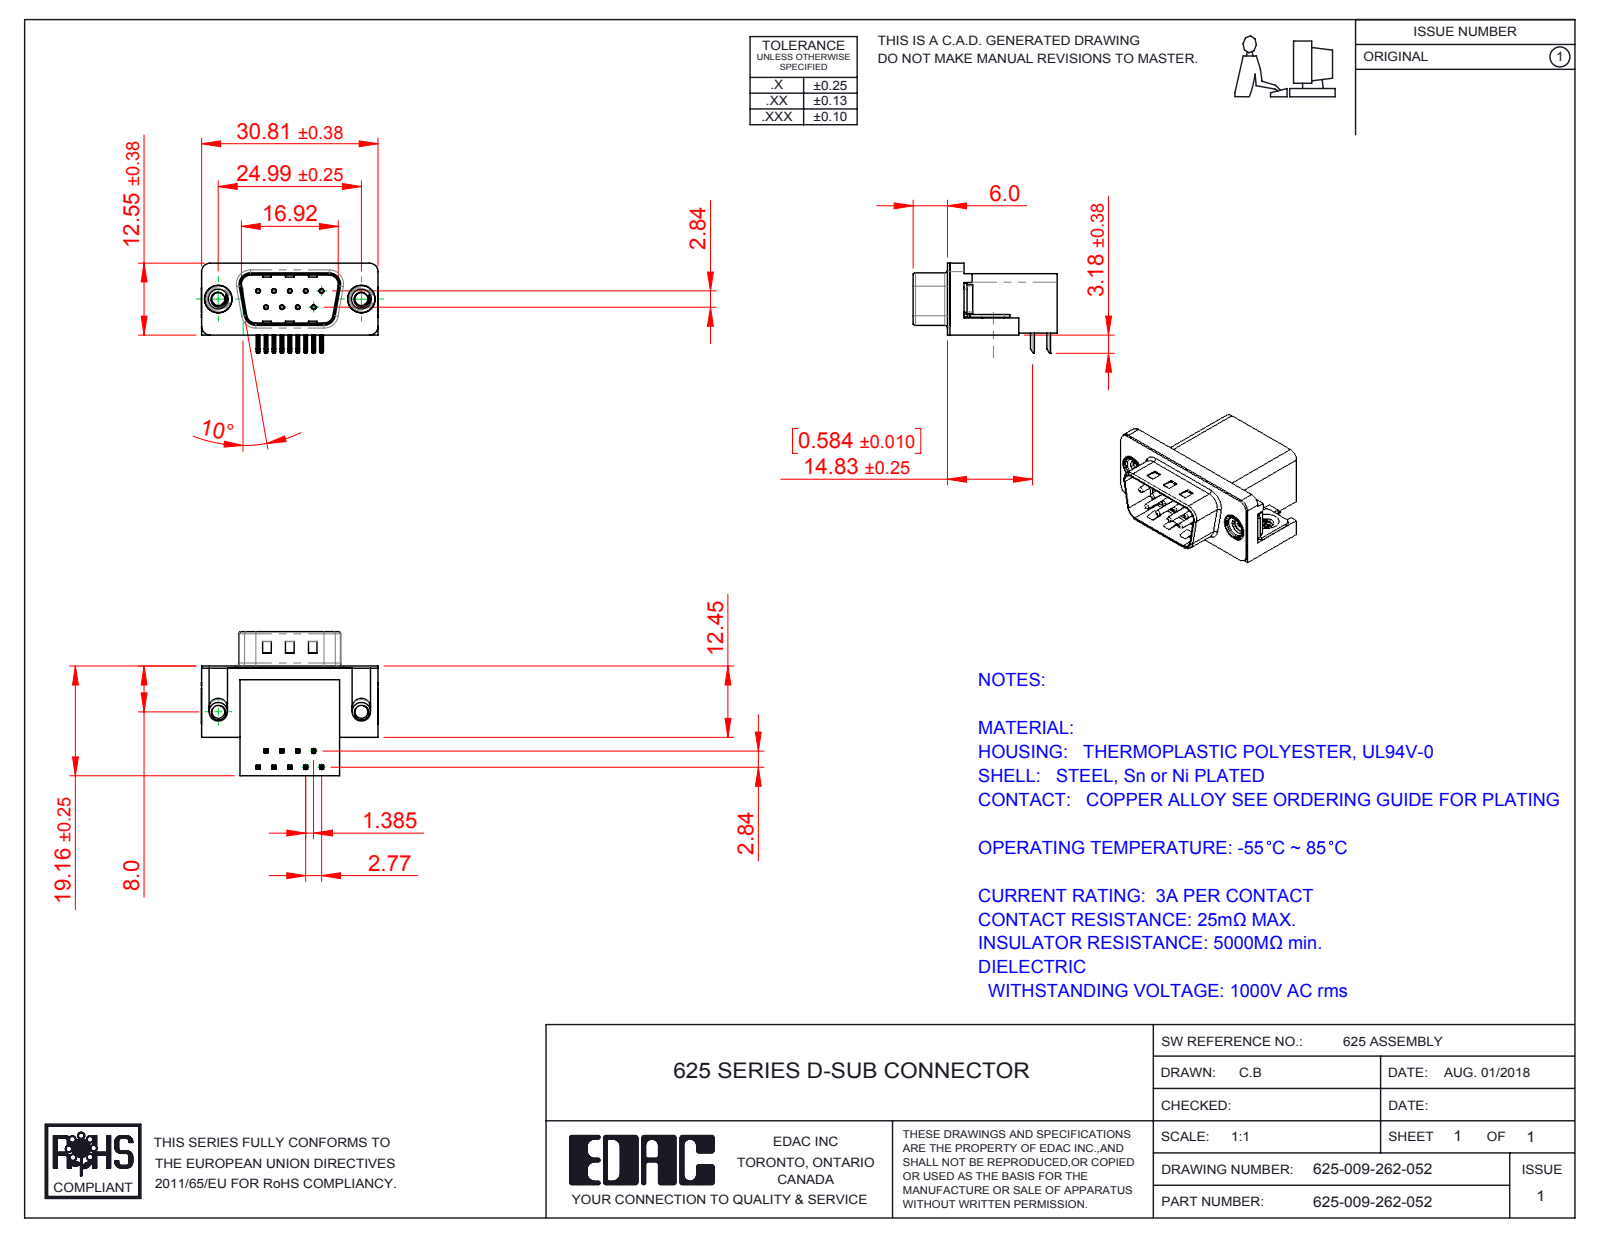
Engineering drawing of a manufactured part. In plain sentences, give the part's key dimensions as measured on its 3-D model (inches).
The part is named "625 Contact Top; 625 4-40 Threaded Rivet; 625 Shell_9 Socket; 625 Housing_9 Socket (+3 more)". Its 3-D file was written by "SolidWorks 2016 (CONFIG_CONTROL_DESIGN)". It is 15 solids with 1025 faces: 575 planar, 329 cylindrical and 121 other. Overall it measures 1.216 by 0.991 by 0.619 inches. Its volume is 0.274 cubic inches and its surface area 7.798 square inches. Round holes: 9 of diameter 0.014, 9 of diameter 0.031, 4 of diameter 0.089, 2 of diameter 0.157, 2 of diameter 0.189, 2 of diameter 0.197. Round bosses or shafts: 9 of diameter 0.03, 2 of diameter 0.193, 2 of diameter 0.187, 2 of diameter 0.154, 2 of diameter 0.128. Partial cylindrical surfaces (rounded edges, fillets, slot ends): 44 of radius 0.01, 18 of radius 0.005, 16 of radius 0.039, 9 of radius 0.02, 8 of radius 0.059, 8 of radius 0.063, 4 of radius 0.035, 4 of radius 0.079. The main face-to-face distances are 0.016, 0.407, 0.739, 0.754, 0.114, 0.64, 0.098, 0.014, 0.421, 0.264. The hole center spacings are 0.124, 0.109, 0.218, 0.198, 0.198, 0.327, 0.294, 0.295.
